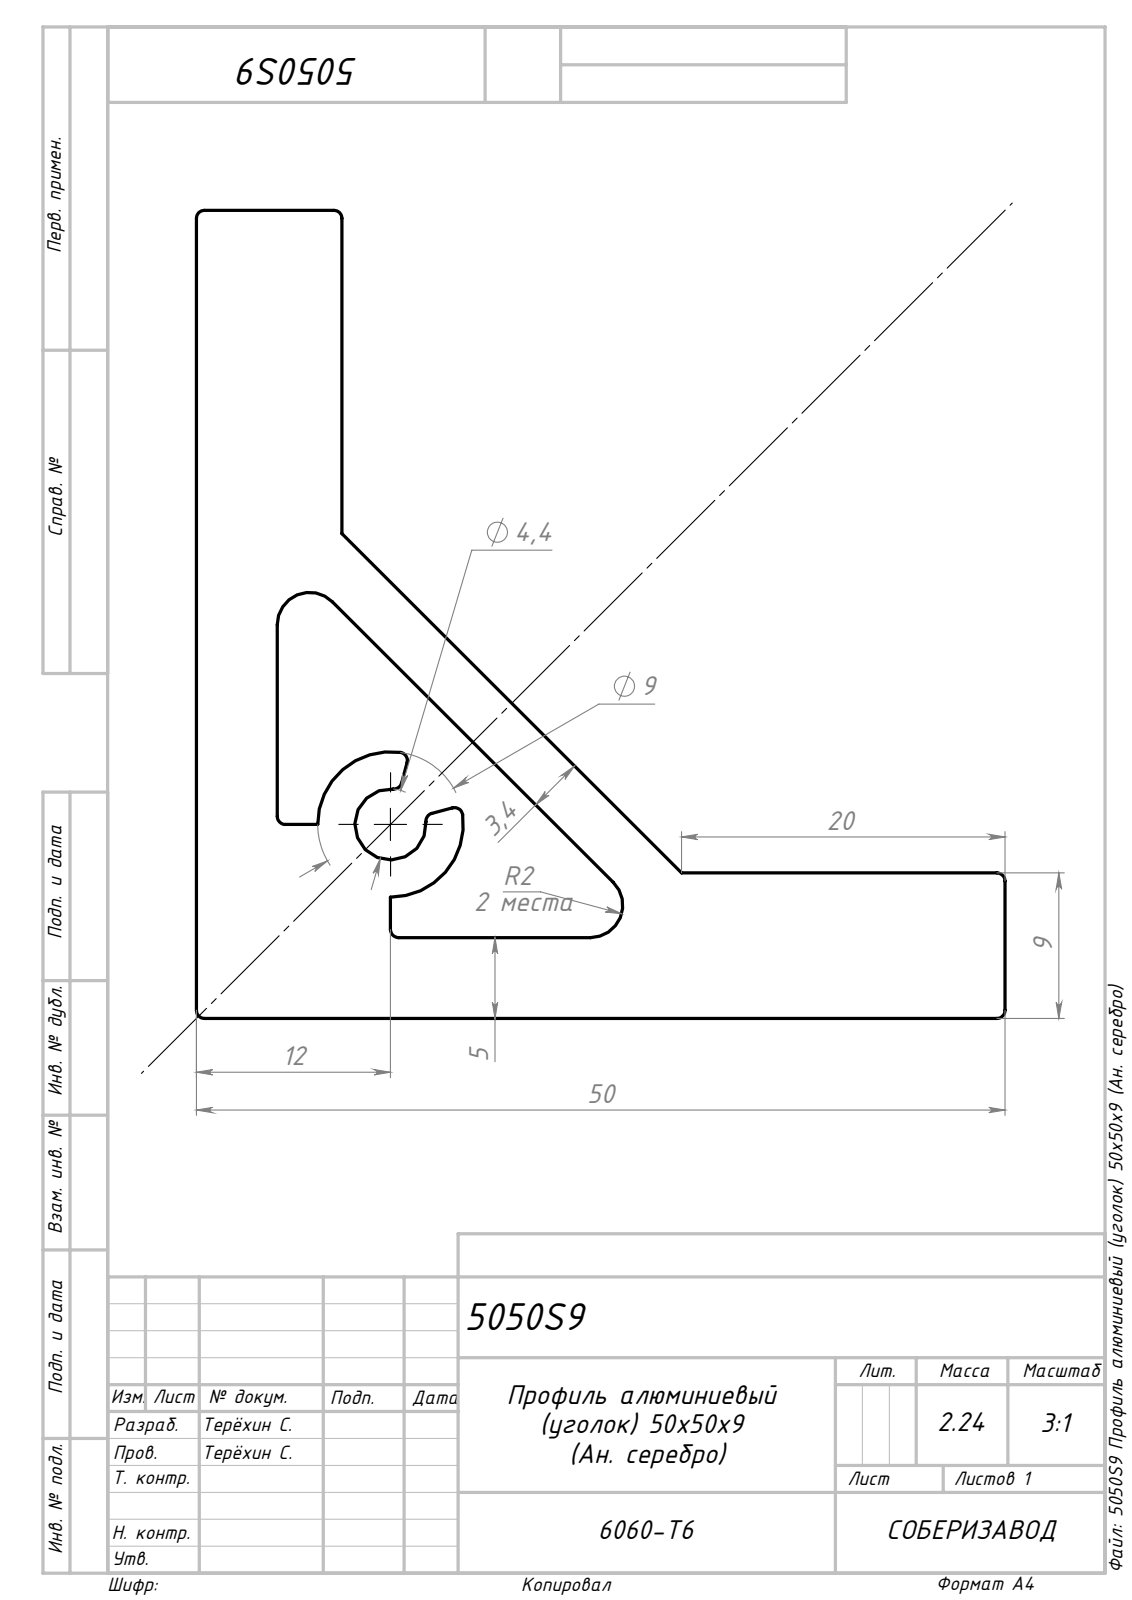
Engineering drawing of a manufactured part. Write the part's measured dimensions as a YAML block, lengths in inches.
part_name: "5050S9 Профиль алюминиевый (уголок) 50х50х9 (Ан. серебро)_00; Сборка2"
step_written_by: "SolidWorks 2022 (AUTOMOTIVE_DESIGN)"
units: inches
bodies: {solids: 1, faces: 36, planar: 16, cylindrical: 20, other: 0}
overall_size: [39.37, 1.969, 1.969]
volume: 50.64
surface_area: 439.2
partial_cylinders:
  - {radius: 0.02, count: 11}
  - {radius: 0.079, count: 2}
  - {radius: 0.087, count: 1}
  - {radius: 0.177, count: 1}
face_to_face_distances: [0.354, 0.134, 0.197, 0.157, 1.969, 1.772, 1.614, 0.472, 0.276, 0.118]
